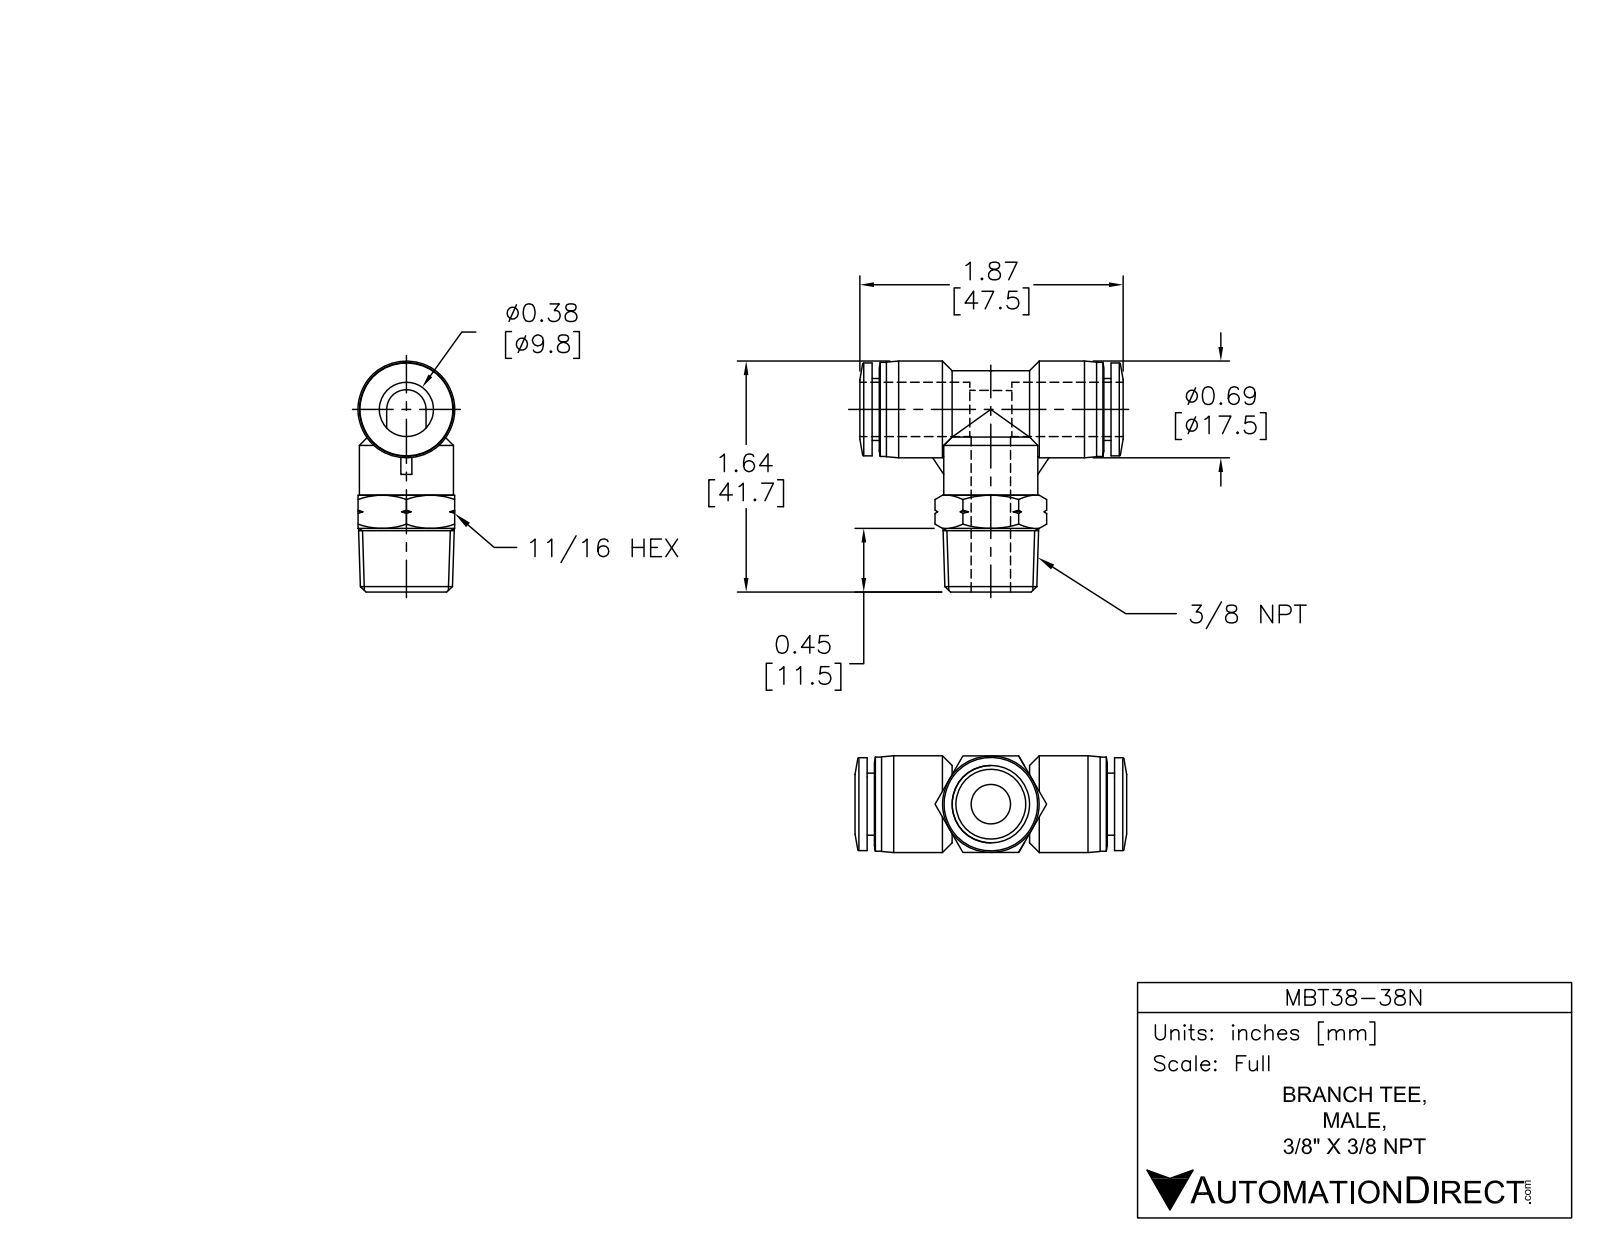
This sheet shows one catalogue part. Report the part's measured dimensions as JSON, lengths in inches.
{"part_name": "MBT38-38N", "step_written_by": "SolidWorks 2015 (AUTOMOTIVE_DESIGN)", "units": "inches", "bodies": {"solids": 1, "faces": 116, "planar": 23, "cylindrical": 31, "other": 62}, "overall_size": [1.874, 1.644, 0.689], "volume_in3": 0.696, "surface_area_in2": 10.5, "round_holes": [[0.276, 2], [0.386, 1]], "round_bosses_or_shafts": [[0.669, 2], [0.689, 1], [0.661, 1], [0.441, 1]], "partial_cylinders_radius": [[0.276, 2]], "face_to_face_distances": [0.687, 0.051, 1.65, 1.701, 1.598, 0.705, 0.996, 0.654, 0.945, 0.291]}
